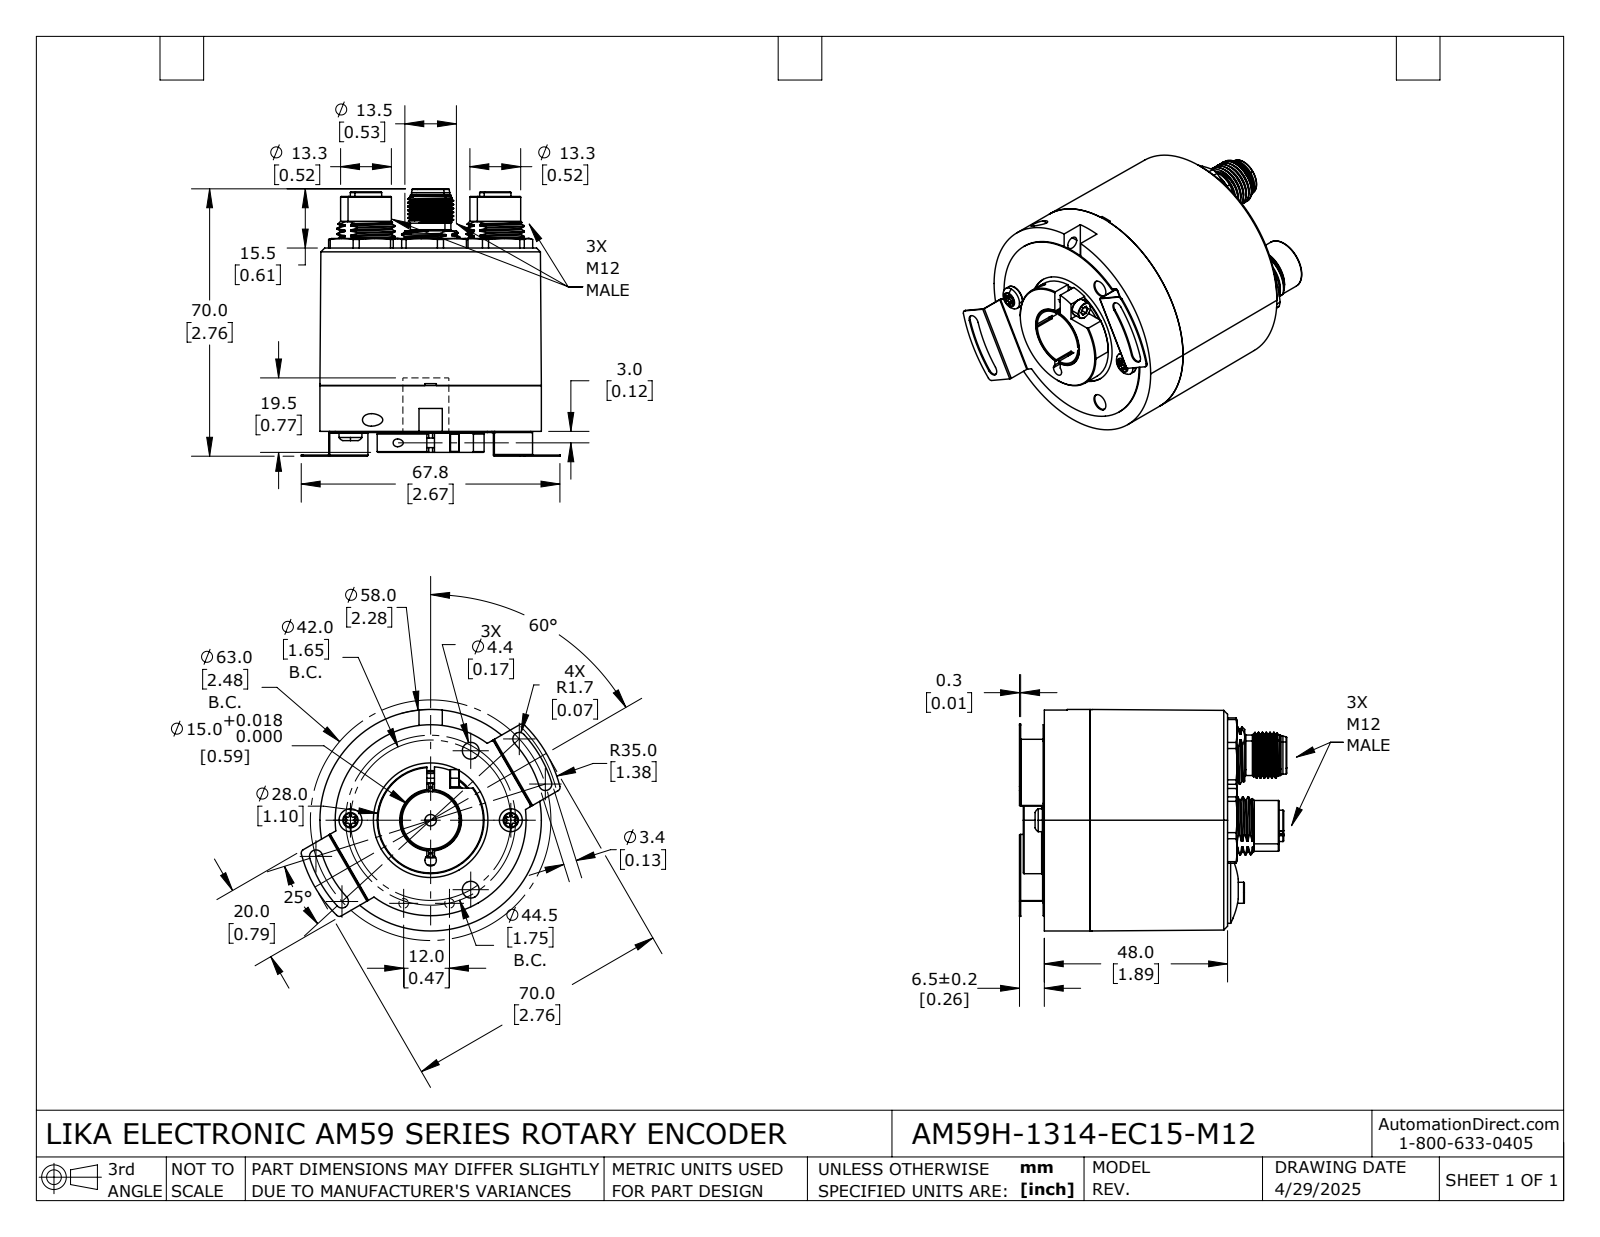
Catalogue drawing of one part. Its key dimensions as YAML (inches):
part_name: "AM59H-1314-EC15-M12"
step_written_by: "SolidWorks 2024 (AUTOMOTIVE_DESIGN)"
units: inches
bodies: {solids: 55, faces: 1648, planar: 438, cylindrical: 595, other: 615}
overall_size: [2.756, 2.669, 2.283]
volume: 3.965
surface_area: 84.73
round_holes:
  - {diameter: 0.079, count: 11}
  - {diameter: 0.047, count: 10}
  - {diameter: 0.098, count: 8}
  - {diameter: 0.081, count: 6}
  - {diameter: 0.138, count: 5}
  - {diameter: 0.063, count: 4}
  - {diameter: 0.492, count: 3}
  - {diameter: 0.126, count: 2}
  - {diameter: 0.173, count: 2}
  - {diameter: 0.382, count: 2}
  - {diameter: 0.429, count: 2}
  - {diameter: 0.041, count: 1}
round_bosses_or_shafts:
  - {diameter: 0.063, count: 12}
  - {diameter: 0.039, count: 12}
  - {diameter: 0.118, count: 8}
  - {diameter: 0.524, count: 3}
  - {diameter: 0.236, count: 3}
  - {diameter: 2.283, count: 1}
  - {diameter: 2.185, count: 1}
  - {diameter: 2.165, count: 1}
partial_cylinders:
  - {radius: 0.039, count: 29}
  - {radius: 0.008, count: 26}
  - {radius: 0.01, count: 12}
  - {radius: 0.017, count: 12}
  - {radius: 0.004, count: 6}
  - {radius: 0.006, count: 4}
  - {radius: 0.012, count: 4}
  - {radius: 0.067, count: 4}
face_to_face_distances: [0.098, 1.791, 1.89, 1.902, 1.803, 0.602, 1.299, 0.02, 0.787, 0.689]
hole_center_spacings: [0.827, 0.209, 0.295, 0.591, 0.791, 0.835, 0.965, 1.27]
